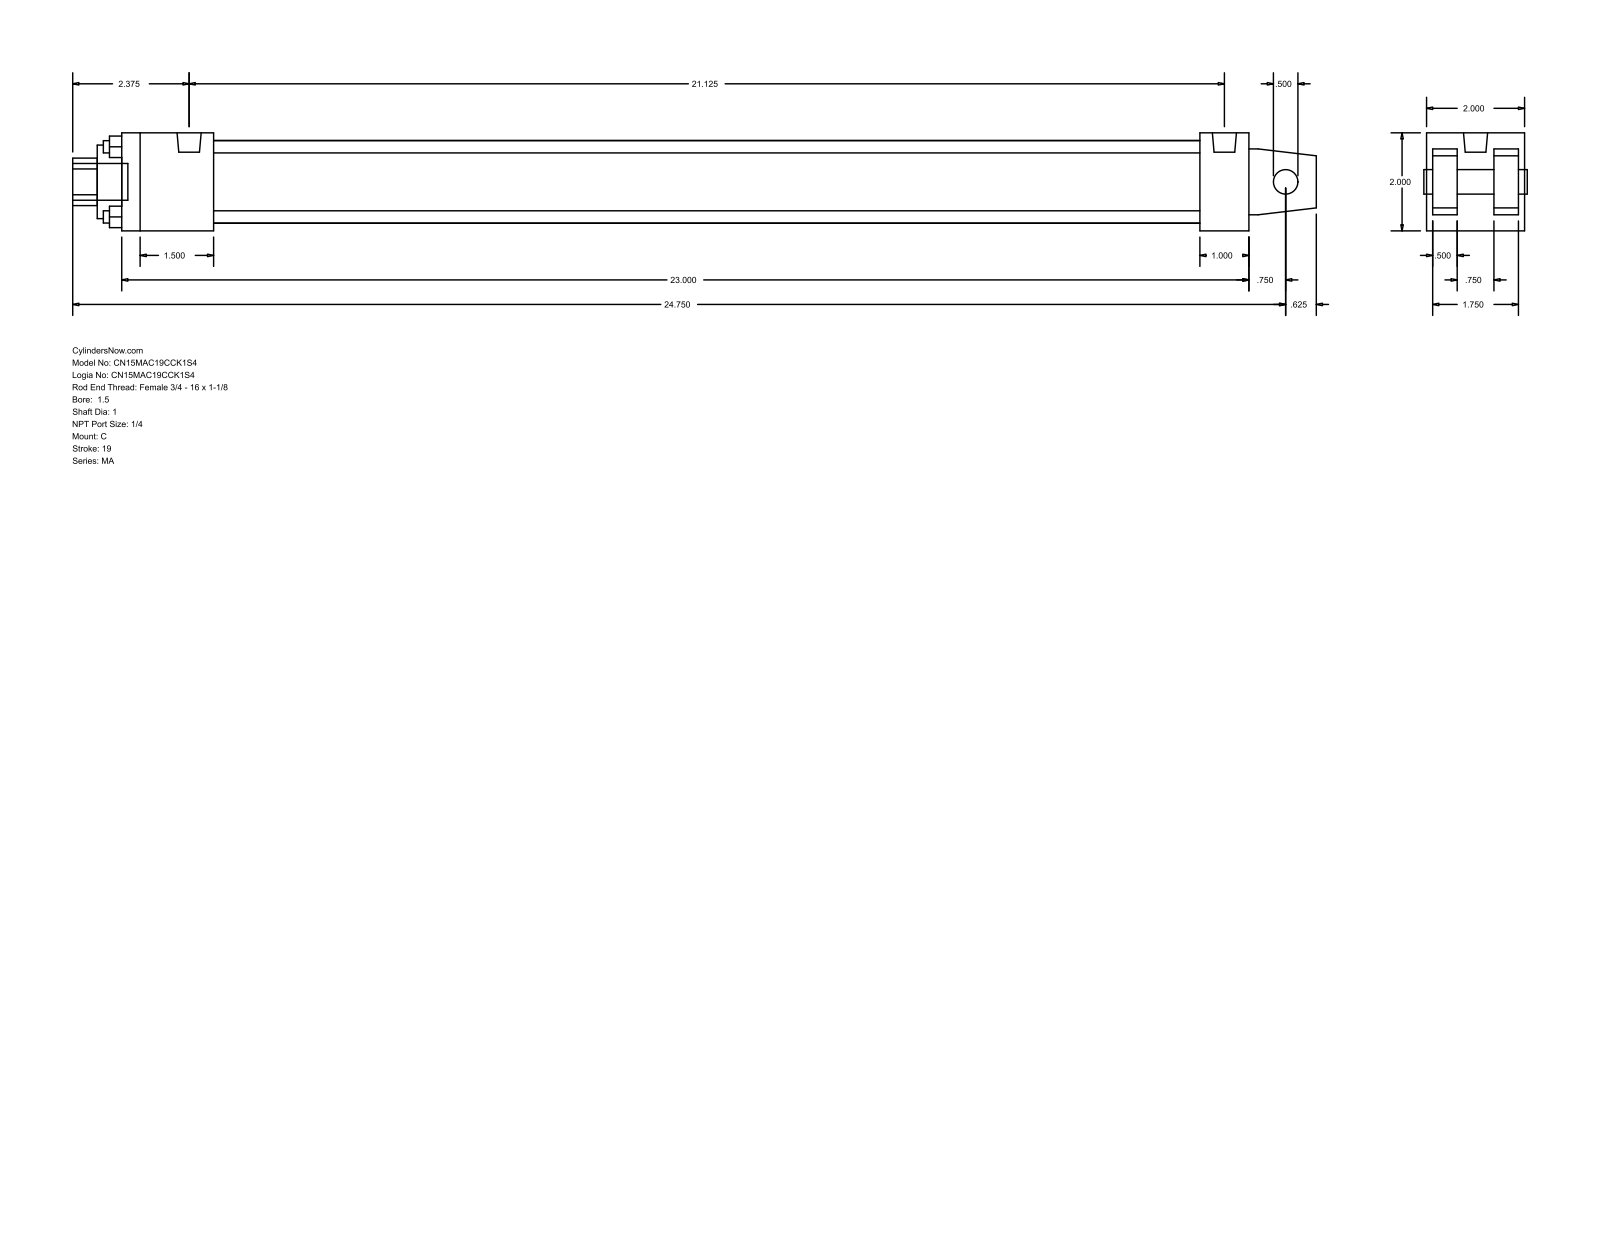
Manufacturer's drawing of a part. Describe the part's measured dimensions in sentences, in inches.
The part is named "MA_C__0150_1". Its 3-D file was written by "GSSL Pune (CONFIG_CONTROL_DESIGN)". It is 0 solids with 103 faces: 76 planar, 27 cylindrical and 0 other. Overall it measures 25.375 by 2 by 2 inches. Round holes: 4 of diameter 0.25, 1 of diameter 0.5, 1 of diameter 1, 1 of diameter 1.5, 1 of diameter 1.69. Round bosses or shafts: 4 of diameter 0.313, 2 of diameter 0.492, 1 of diameter 0.75. Partial cylindrical surfaces (rounded edges, fillets, slot ends): 1 of radius 0.484. The main face-to-face distances are 2, 1.875, 0.5, 0.125, 0.625, 1.375, 1.25, 1.75, 23, 1. The hole center spacings are 1.011, 1.43, 2.022.
